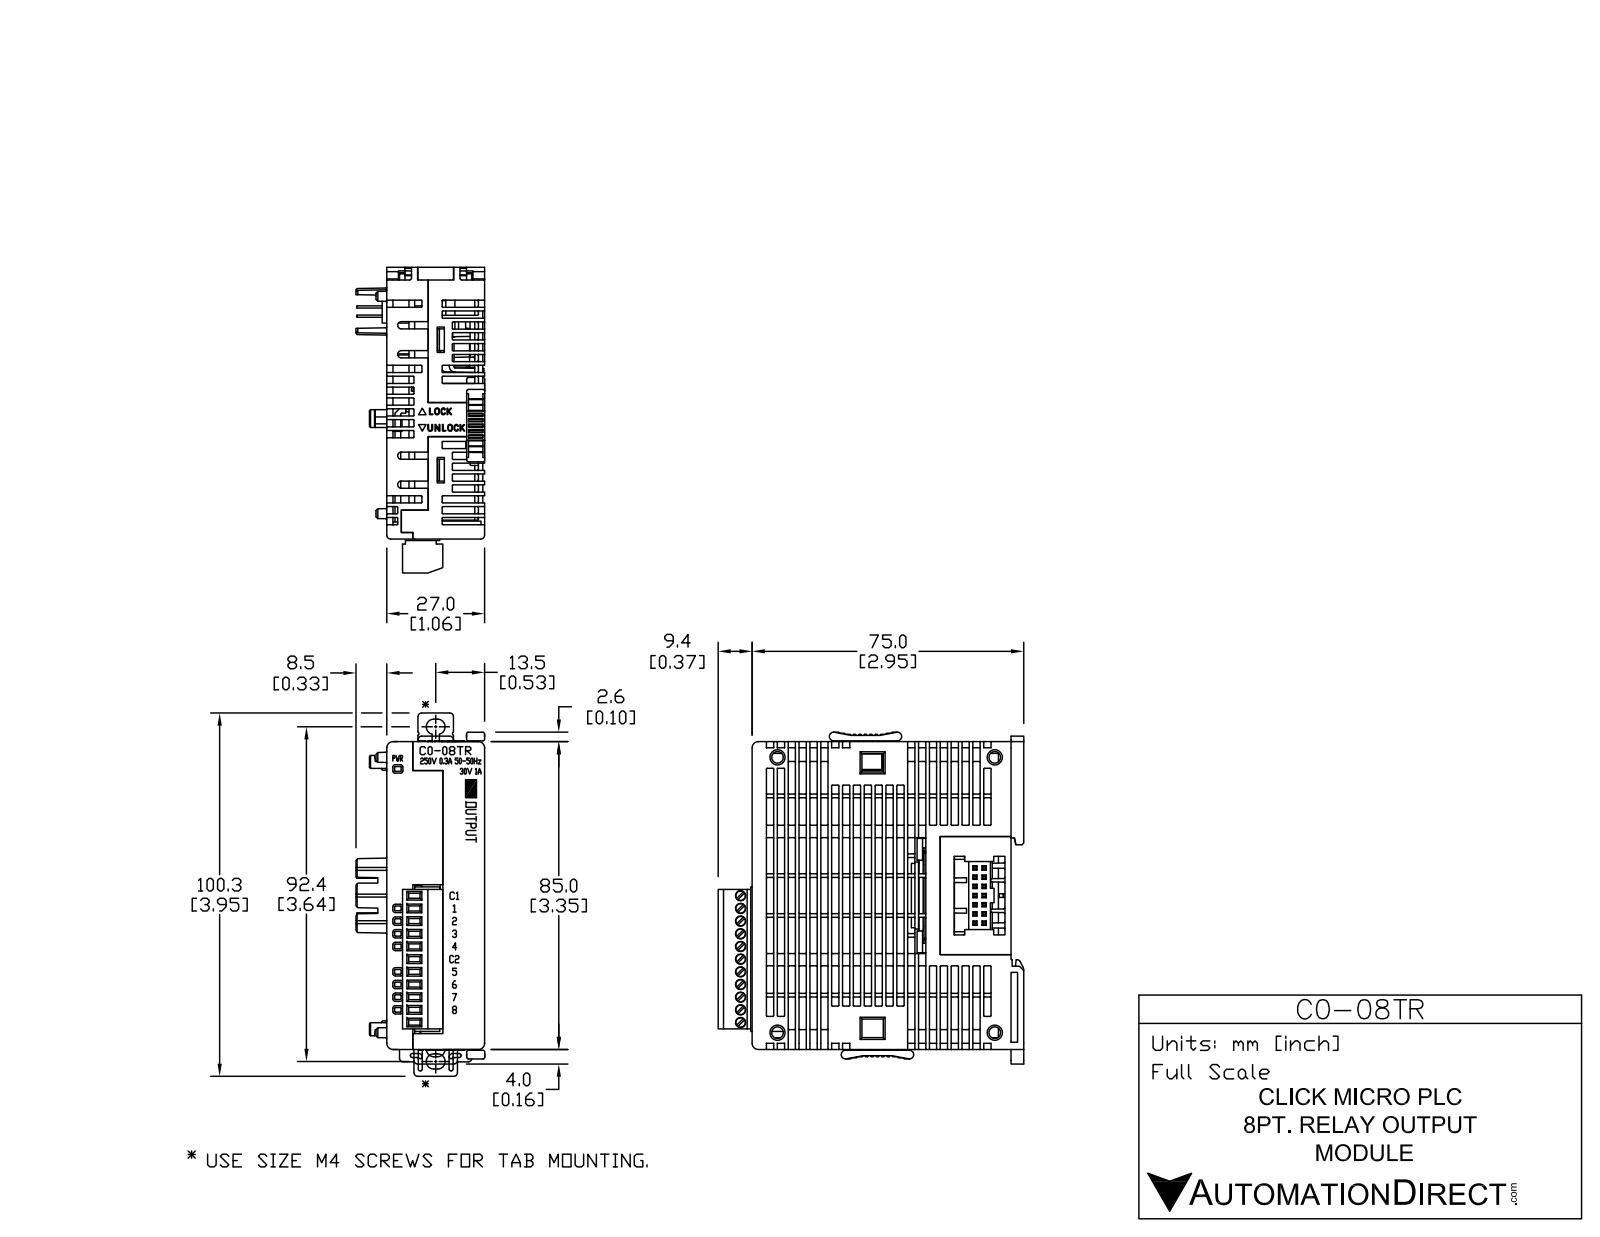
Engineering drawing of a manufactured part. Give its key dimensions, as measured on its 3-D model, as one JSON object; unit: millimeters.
{"part_name": "C0-08TR", "step_written_by": "SolidWorks 2009 (AUTOMOTIVE_DESIGN)", "units": "millimeters", "bodies": {"solids": 1, "faces": 3689, "planar": 2637, "cylindrical": 968, "other": 84}, "overall_size": [91.6, 84.4, 35.55], "volume_mm3": 162505, "surface_area_mm2": 31767, "round_holes": [[1, 11], [2.8, 11], [3.2, 4], [2, 2]], "round_bosses_or_shafts": [[2.6, 11], [1.9, 1]], "partial_cylinders_radius": [[0.2, 570], [0.5, 43], [0.3, 22], [1, 18], [1.2, 12], [2.8, 11], [1.7, 6], [2.1, 4]], "face_to_face_distances": [27.01, 0.5, 0.51, 26.5, 71.5, 1.7, 85, 26.3, 26.81, 84.5], "hole_center_spacings": [3.5, 7, 10.5, 14, 17.5, 21, 24.5, 28]}
